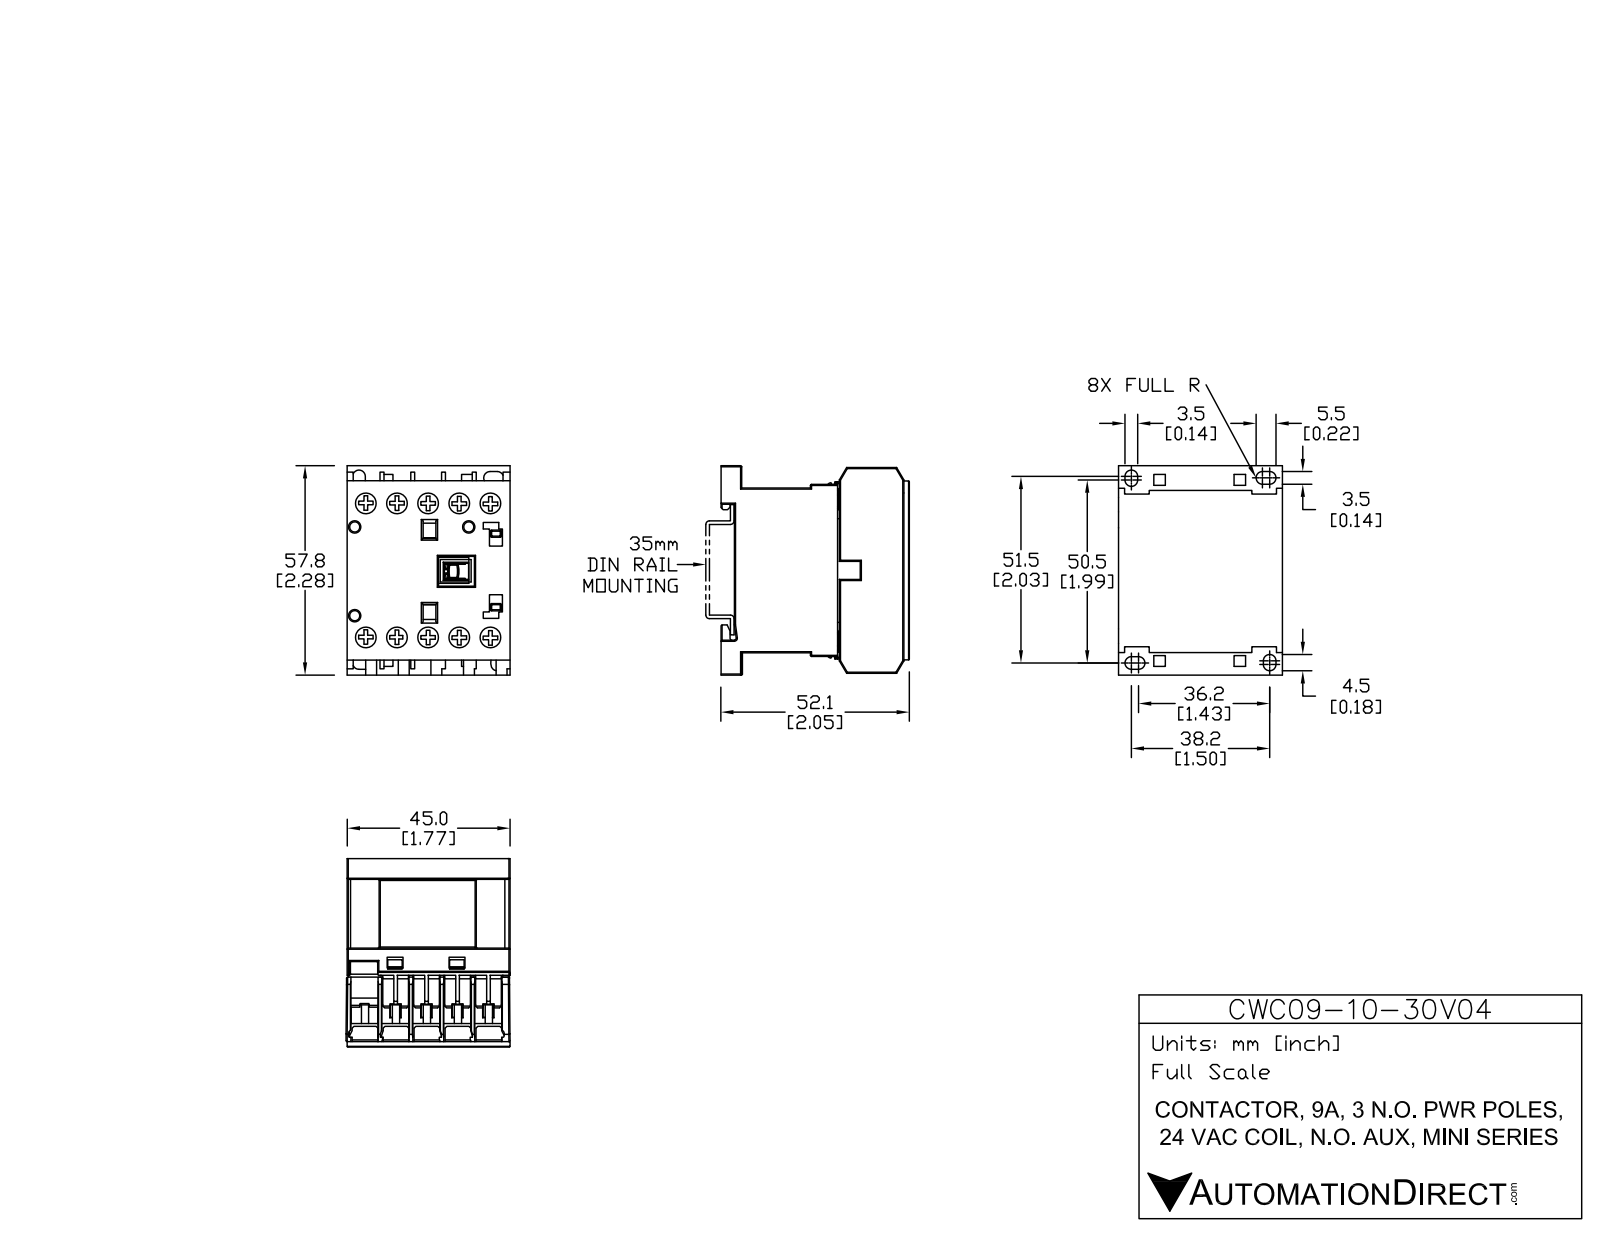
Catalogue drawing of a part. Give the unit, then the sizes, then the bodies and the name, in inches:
Units: inches
Overall size (bounding box): 2.285 × 2.052 × 1.801
Round holes (diameter × count): ⌀0.244 ×10, ⌀0.11 ×3
Round bosses / shafts (diameter × count): ⌀0.232 ×10
Partial cylindrical surfaces — rounded edges, fillets, slot ends (radius × count): R0.012 ×20, R0.068 ×6, R0.068 ×2, R0.013 ×1, R0.017 ×1, R0.022 ×1
Main face-to-face distances: 0.325, 1.791, 0.049, 0.65, 0.374, 0.217, 0.699, 0.202, 0.419, 0.276
Hole centre spacings: 0.337, 1.494, 0.673, 1.603, 1.455, 1.01, 1.771, 0.272
Volume: 5.927 in³ · Surface area: 47.18 in²
Bodies: 15 solids, 535 faces (445 planar, 90 cylindrical, 0 other)
Part name (STEP PRODUCT): CWC09-10-30V04
STEP written by: SolidWorks 2013 (AUTOMOTIVE_DESIGN)
